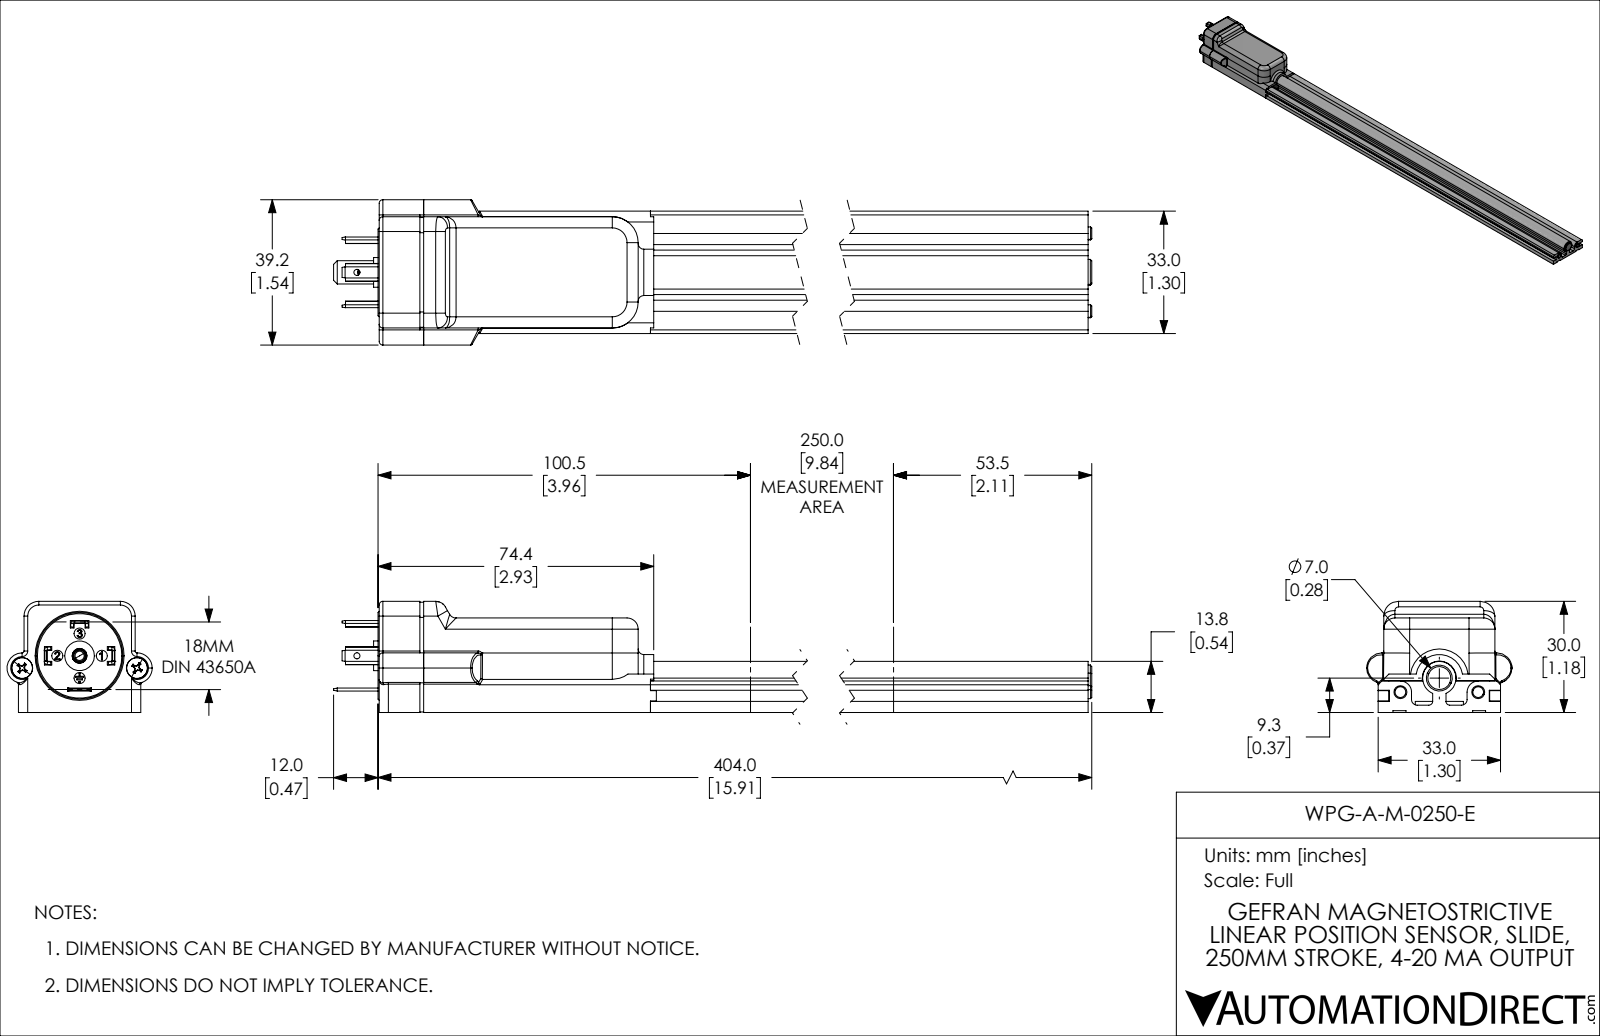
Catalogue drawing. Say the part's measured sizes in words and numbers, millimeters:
The part is named "WPG-A-M-0250-E". Its 3-D file was written by "SolidWorks 2021 (CONFIG_CONTROL_DESIGN)". It is 15 solids with 589 faces: 371 planar, 139 cylindrical and 79 other. Overall it measures 416 by 39.2 by 30 millimeters. Its volume is 136 562 cubic millimeters and its surface area 60 628 square millimeters. Round holes: 5 of diameter 3, 2 of diameter 1.5, 2 of diameter 1.65, 2 of diameter 3.2, 2 of diameter 5.7, 1 of diameter 1.6, 1 of diameter 2.5, 1 of diameter 4. Round bosses or shafts: 2 of diameter 5.6, 2 of diameter 3.5, 2 of diameter 2.85, 1 of diameter 9, 1 of diameter 8, 1 of diameter 7, 1 of diameter 5.3, 1 of diameter 3.94. Partial cylindrical surfaces (rounded edges, fillets, slot ends): 8 of radius 0.5, 8 of radius 3, 6 of radius 0.85, 5 of radius 1, 4 of radius 0.8, 4 of radius 1.5, 4 of radius 4.1, 4 of radius 7. The main face-to-face distances are 3, 1, 2.5, 1.5, 5.5, 6, 8.5, 30, 0.5, 8. The hole center spacings are 6, 8.49, 10.06, 12, 12.3, 15.73, 15.85, 18.08.
